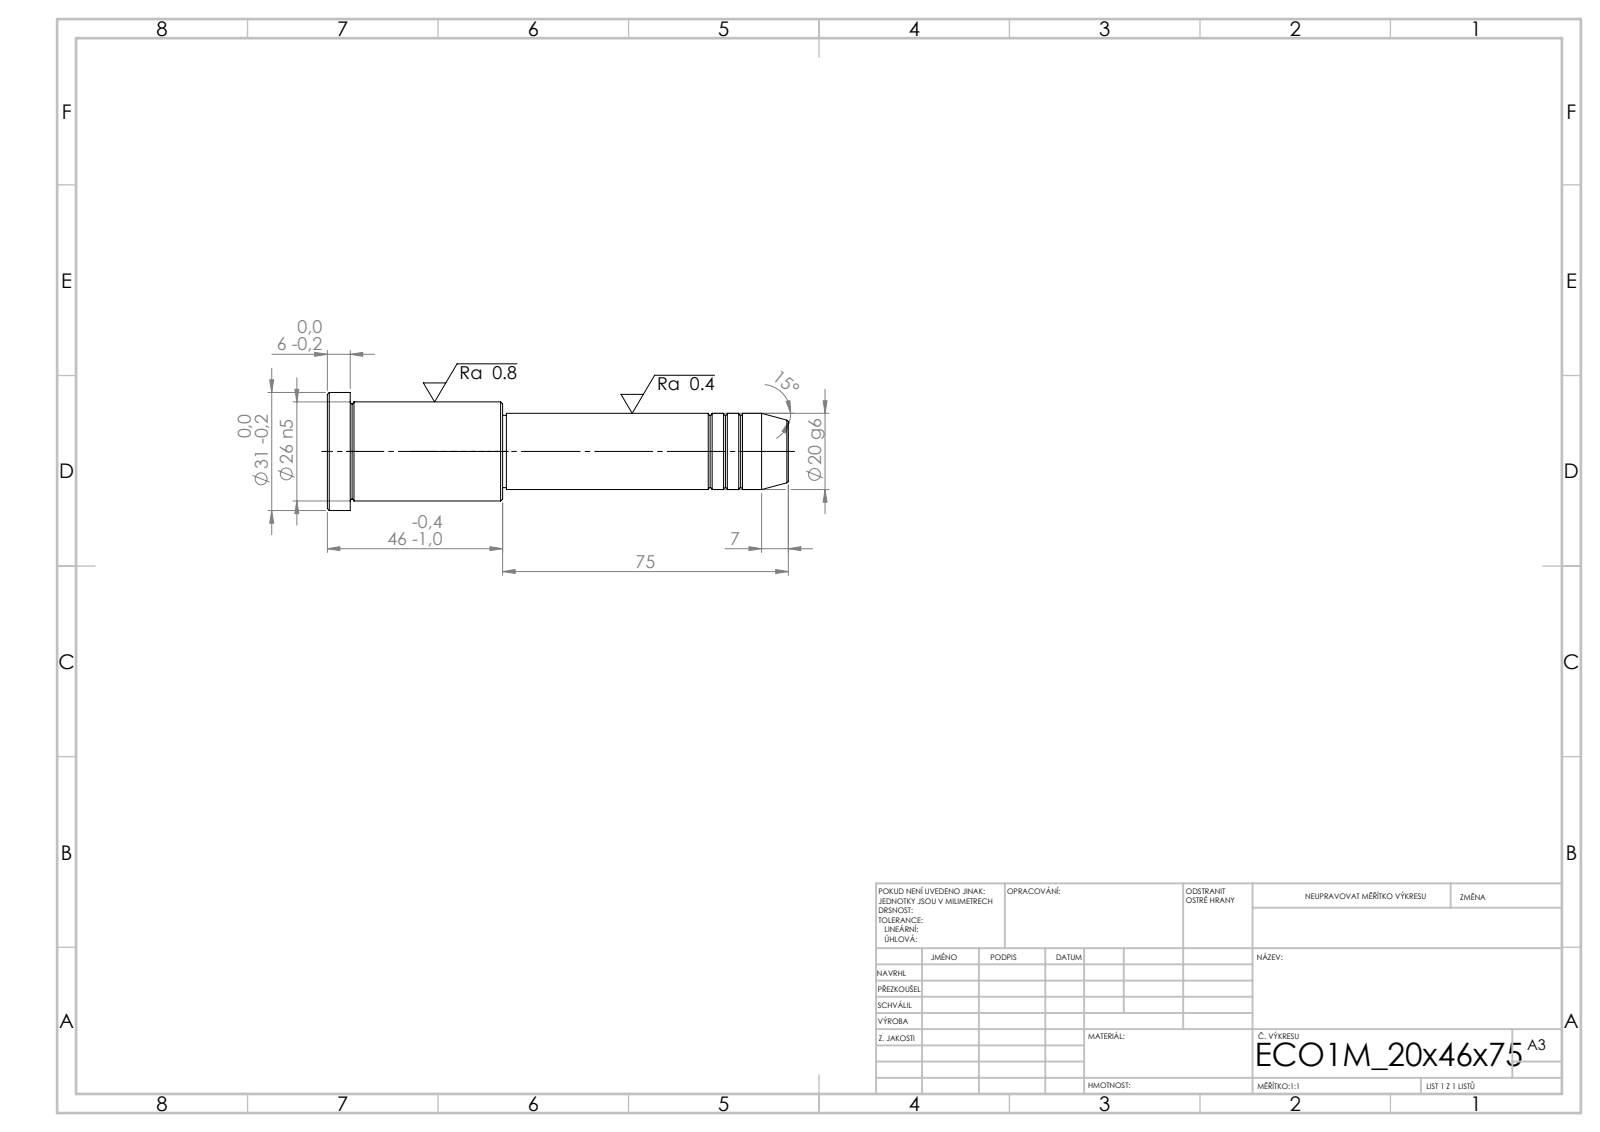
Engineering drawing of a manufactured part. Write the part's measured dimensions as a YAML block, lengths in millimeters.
step_written_by: "SolidWorks 2019 (CONFIG_CONTROL_DESIGN)"
units: millimeters
bodies: {solids: 1, faces: 43, planar: 5, cylindrical: 14, other: 24}
overall_size: [121, 31, 31]
volume: 48783
surface_area: 10080
round_bosses_or_shafts:
  - {diameter: 31, count: 1}
  - {diameter: 26, count: 1}
  - {diameter: 20, count: 1}
  - {diameter: 19, count: 1}
face_to_face_distances: [6, 40, 46, 75, 115, 121, 74, 1, 41, 47]
